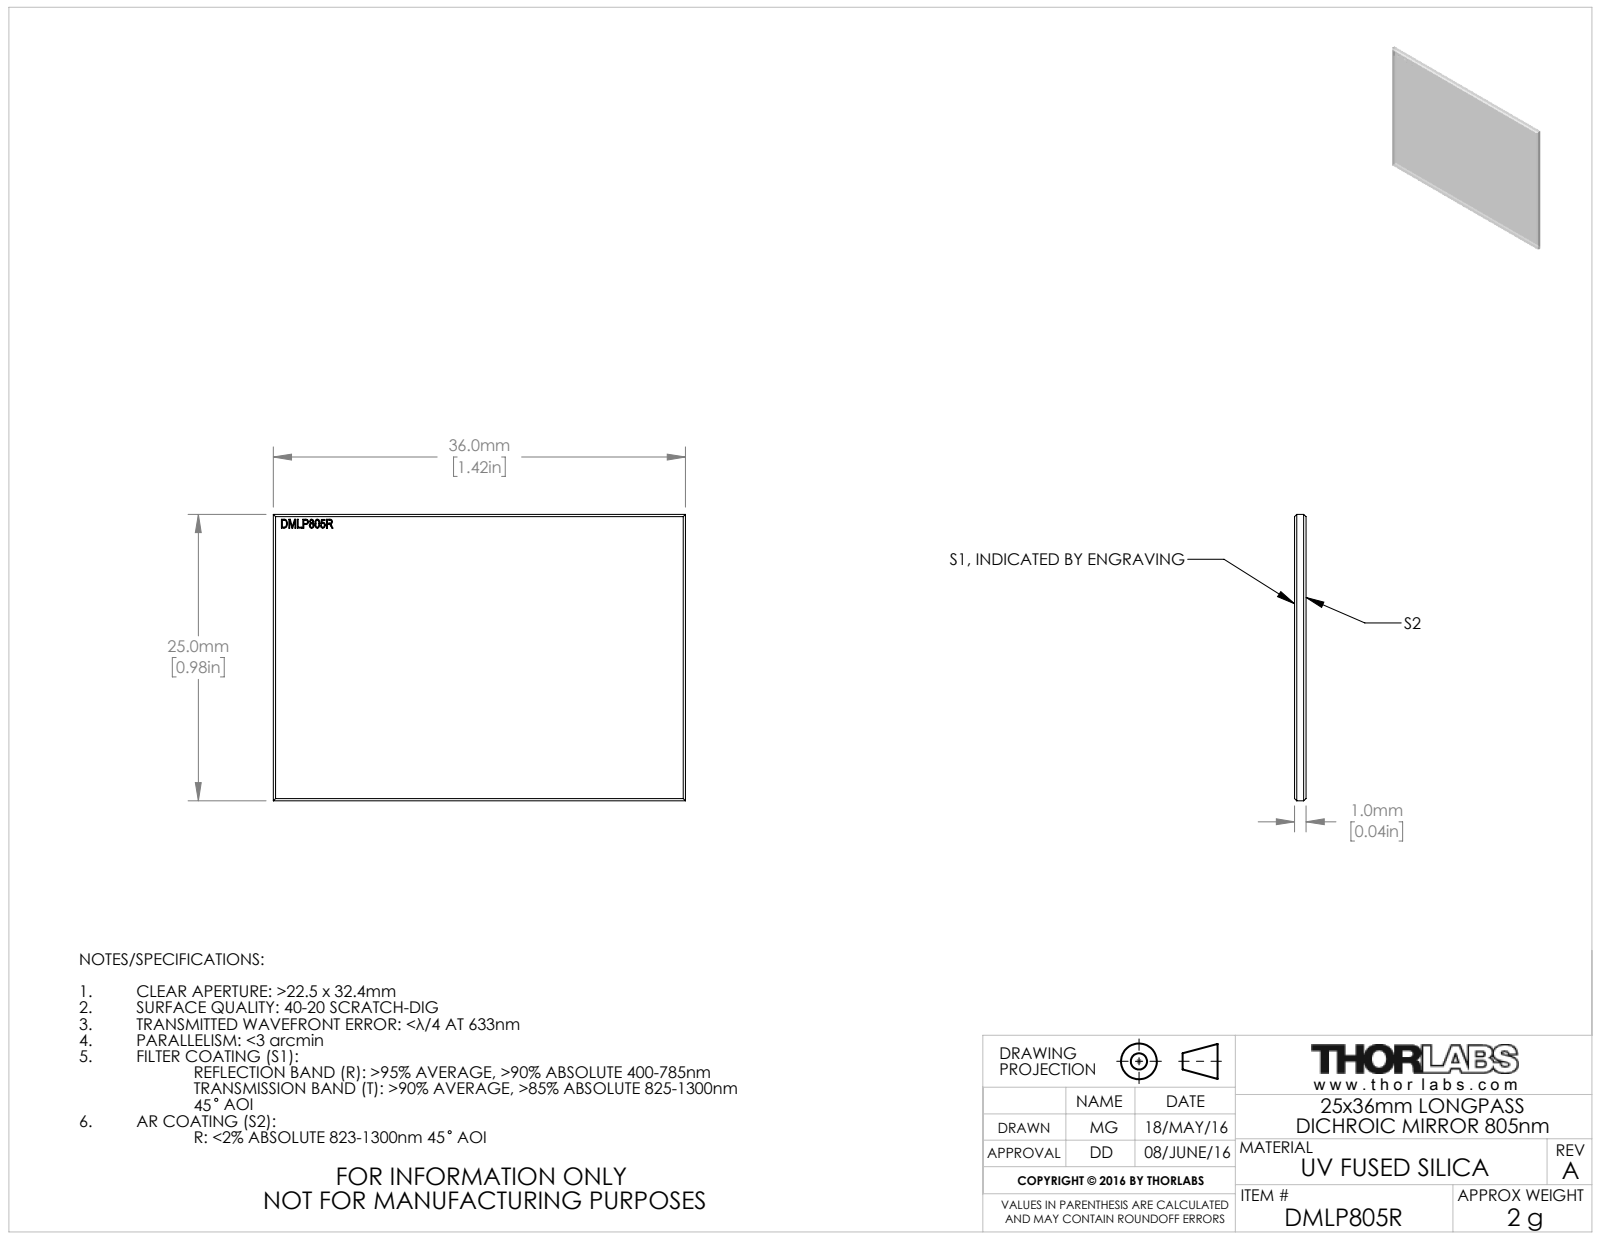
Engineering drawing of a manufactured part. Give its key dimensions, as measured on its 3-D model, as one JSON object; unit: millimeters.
{"part_name": "TTN045184-E0W", "step_written_by": "SolidWorks 2016 (CONFIG_CONTROL_DESIGN)", "units": "millimeters", "bodies": {"solids": 1, "faces": 133, "planar": 80, "cylindrical": 0, "other": 53}, "overall_size": [36, 25, 1], "volume_mm3": 895, "surface_area_mm2": 1894, "face_to_face_distances": [1, 25, 18.1, 36, 25.88, 0.99, 0.53, 0.72, 0.74, 0.64]}
